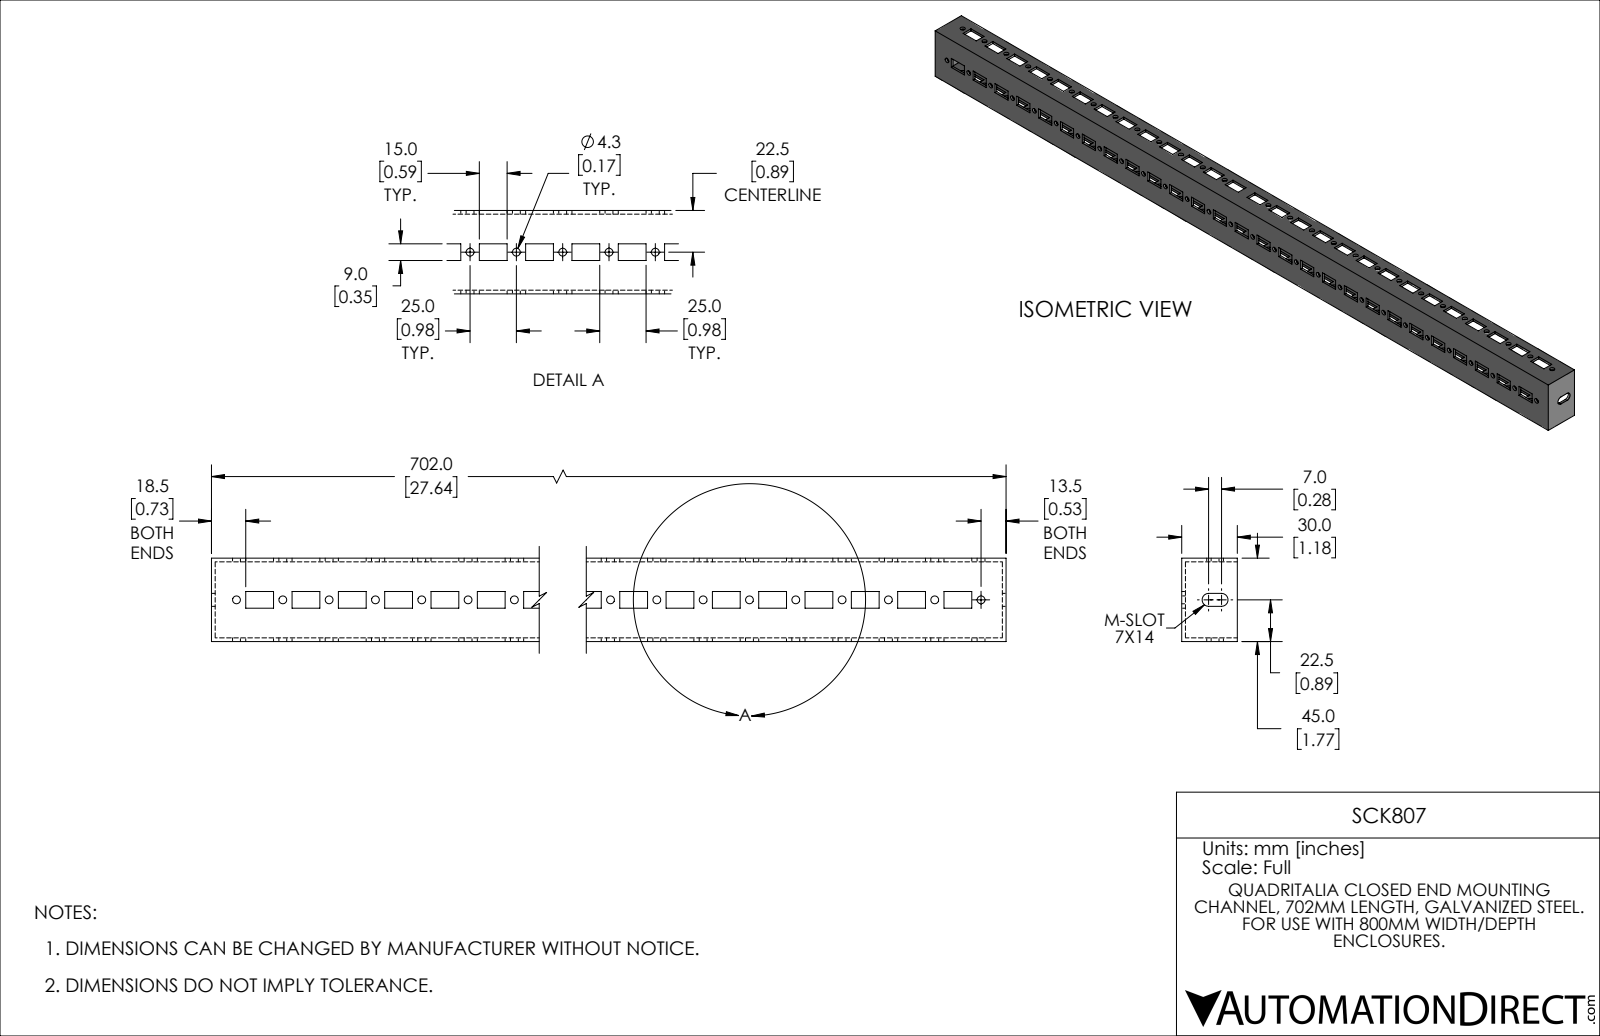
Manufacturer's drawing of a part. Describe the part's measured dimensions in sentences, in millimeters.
The part is named "SCK807". Its 3-D file was written by "SolidWorks 2021 (CONFIG_CONTROL_DESIGN)". It is 1 solid with 425 faces: 339 planar, 86 cylindrical and 0 other. Overall it measures 702 by 45 by 30 millimeters. Its volume is 121 900 cubic millimeters and its surface area 135 000 square millimeters. Round holes: 55 of diameter 4.2. Partial cylindrical surfaces (rounded edges, fillets, slot ends): 2 of radius 3.5. The main face-to-face distances are 2, 43, 45, 41, 30, 28, 9, 25, 700, 22.5. The hole center spacings are 25, 50, 75, 100, 125, 150, 175, 200.
